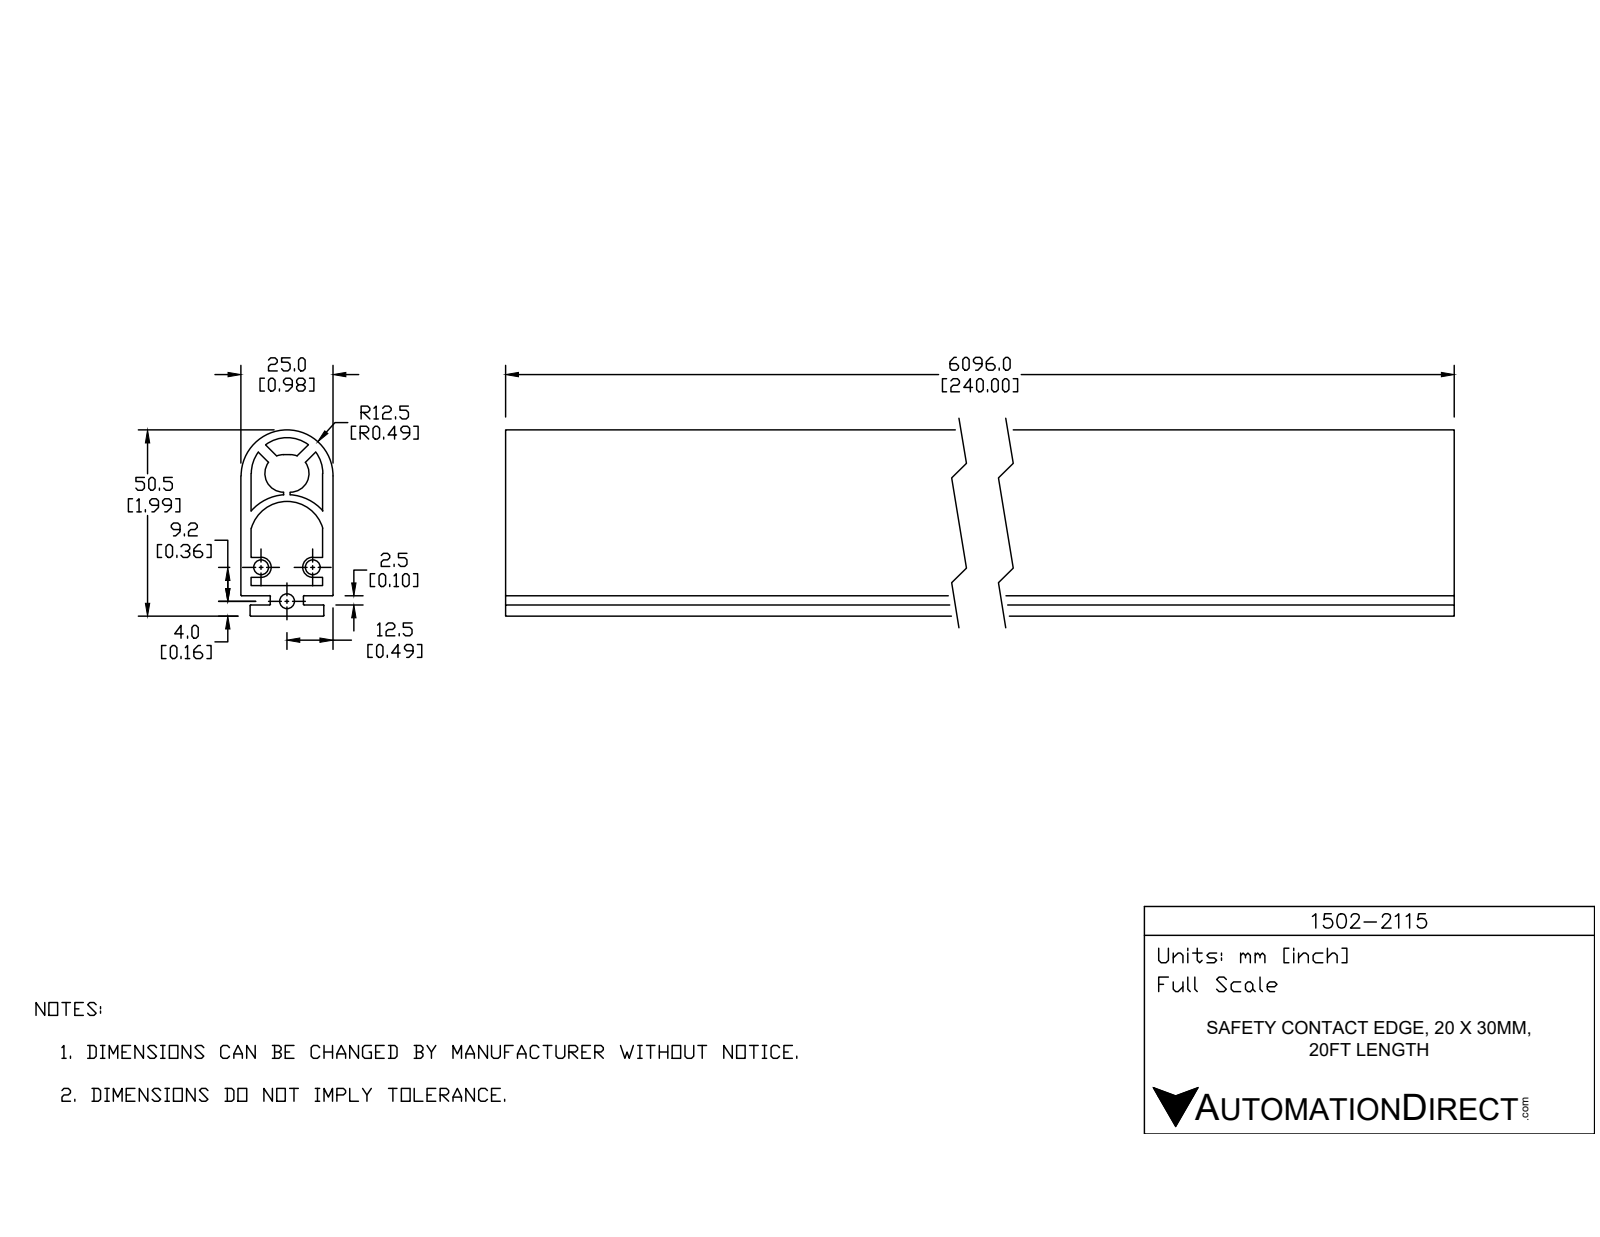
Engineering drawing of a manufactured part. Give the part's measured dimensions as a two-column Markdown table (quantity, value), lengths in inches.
| quantity | value |
| --- | --- |
| part name | 1502-2115 |
| STEP written by | SolidWorks 2017 (AUTOMOTIVE_DESIGN) |
| units | inches |
| bodies | 1 solid, 62 faces (31 planar, 31 cylindrical, 0 other) |
| overall size | 24 × 1.988 × 0.984 |
| volume | 21.87 in³ |
| surface area | 383.4 in² |
| round holes (diameter × count) | 0.157 × 3 |
| partial cylindrical surfaces (radius × count) | 0.008 × 10, 0.106 × 2, 0.202 × 2, 0.382 × 1, 0.398 × 1, 0.492 × 1, 0.508 × 1 |
| main face-to-face distances | 0.11, 0.874, 0.984, 0.764, 0.217, 0.327, 0.098, 0.118, 0.209, 0.11 |
| hole center spacings | 0.456, 0.551 |
